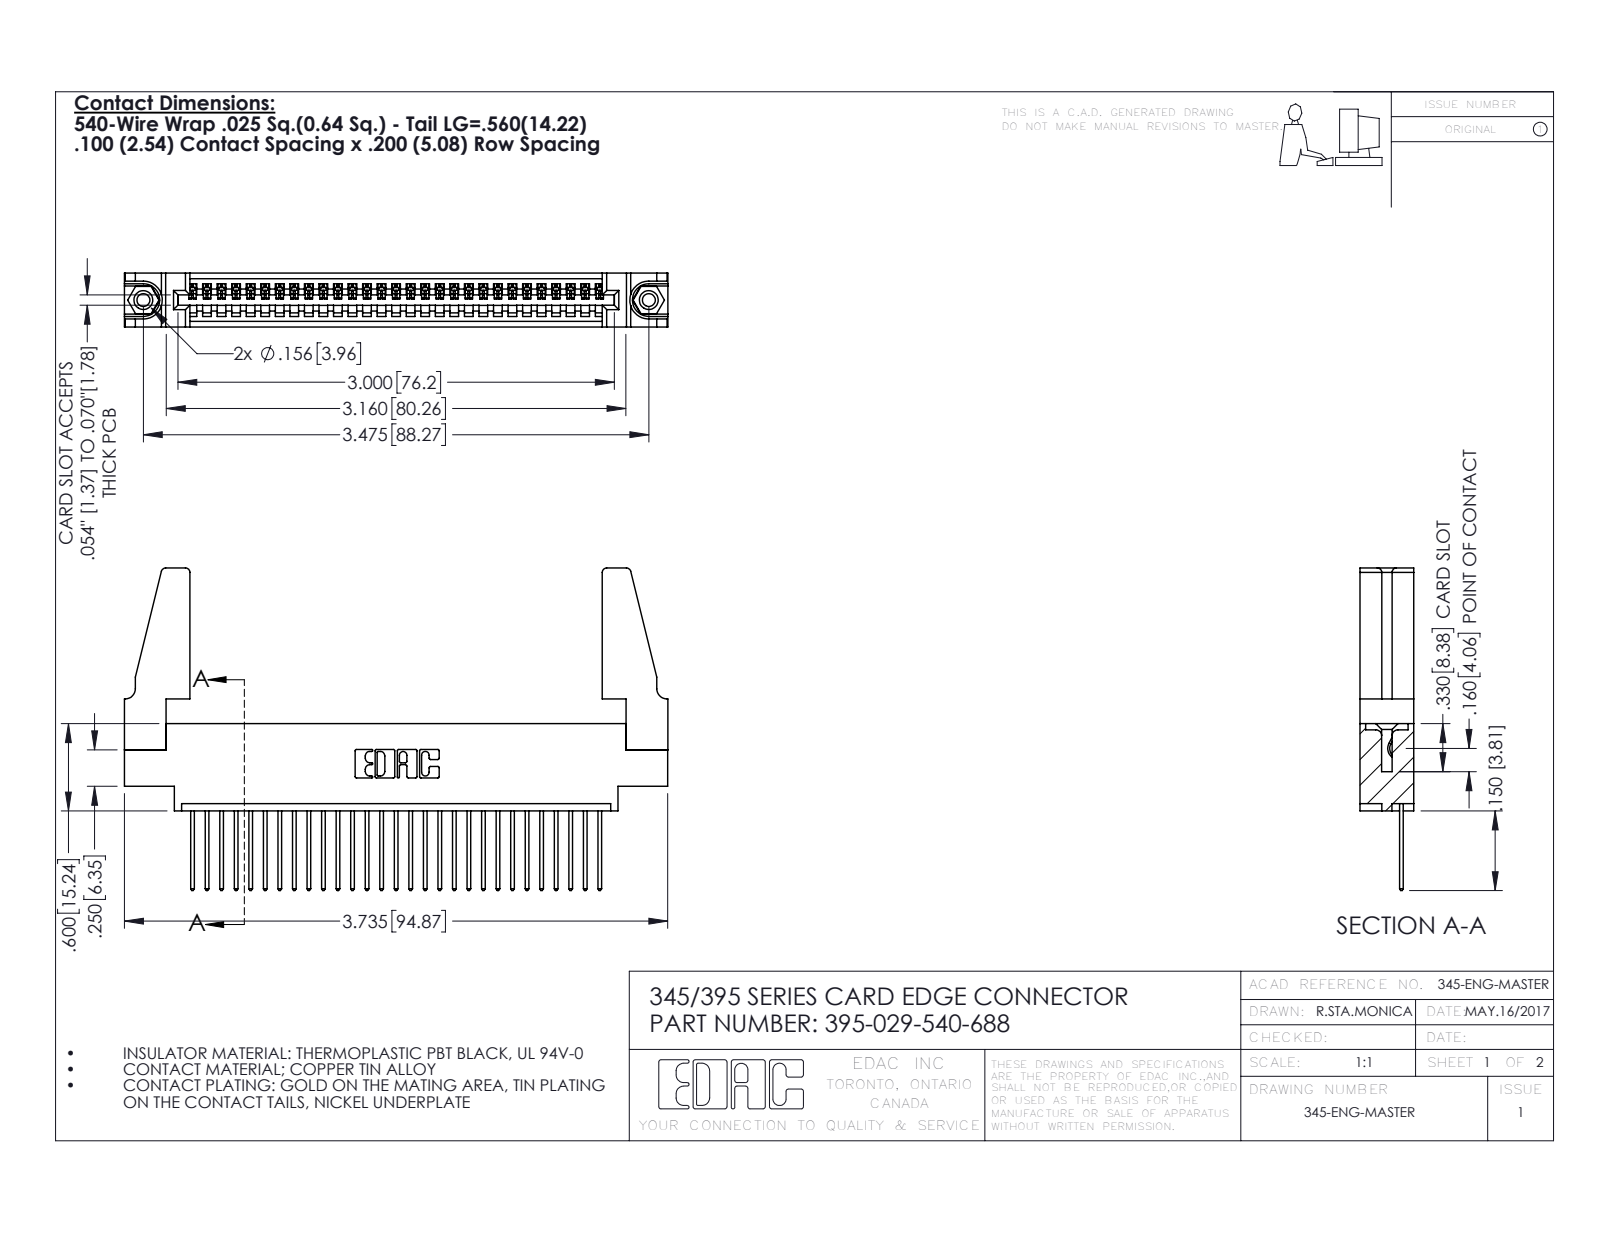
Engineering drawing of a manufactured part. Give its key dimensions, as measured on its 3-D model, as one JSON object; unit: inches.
{"part_name": "395-029-540-688; 345-250-001_345-250-001-102; 345-292-001_345-293-140; 345-220-078_345-220-088 (+1 more)", "step_written_by": "SolidWorks 2016 (CONFIG_CONTROL_DESIGN)", "units": "inches", "bodies": {"solids": 34, "faces": 1936, "planar": 1316, "cylindrical": 604, "other": 16}, "overall_size": [3.736, 2.217, 0.37], "volume_in3": 0.737, "surface_area_in2": 23.4, "round_holes": [[0.089, 2], [0.125, 2], [0.156, 2], [0.064, 1]], "round_bosses_or_shafts": [[0.155, 2]], "partial_cylinders_radius": [[0.006, 58], [0.01, 58], [0.01, 22], [0.03, 8], [0.007, 6], [0.031, 6], [0.026, 3], [0.031, 2]], "face_to_face_distances": [0.072, 0.37, 0.298, 0.098, 0.272, 0.025, 0.2, 0.225, 0.175, 0.149], "hole_center_spacings": [0.27, 3.24, 3.475]}
